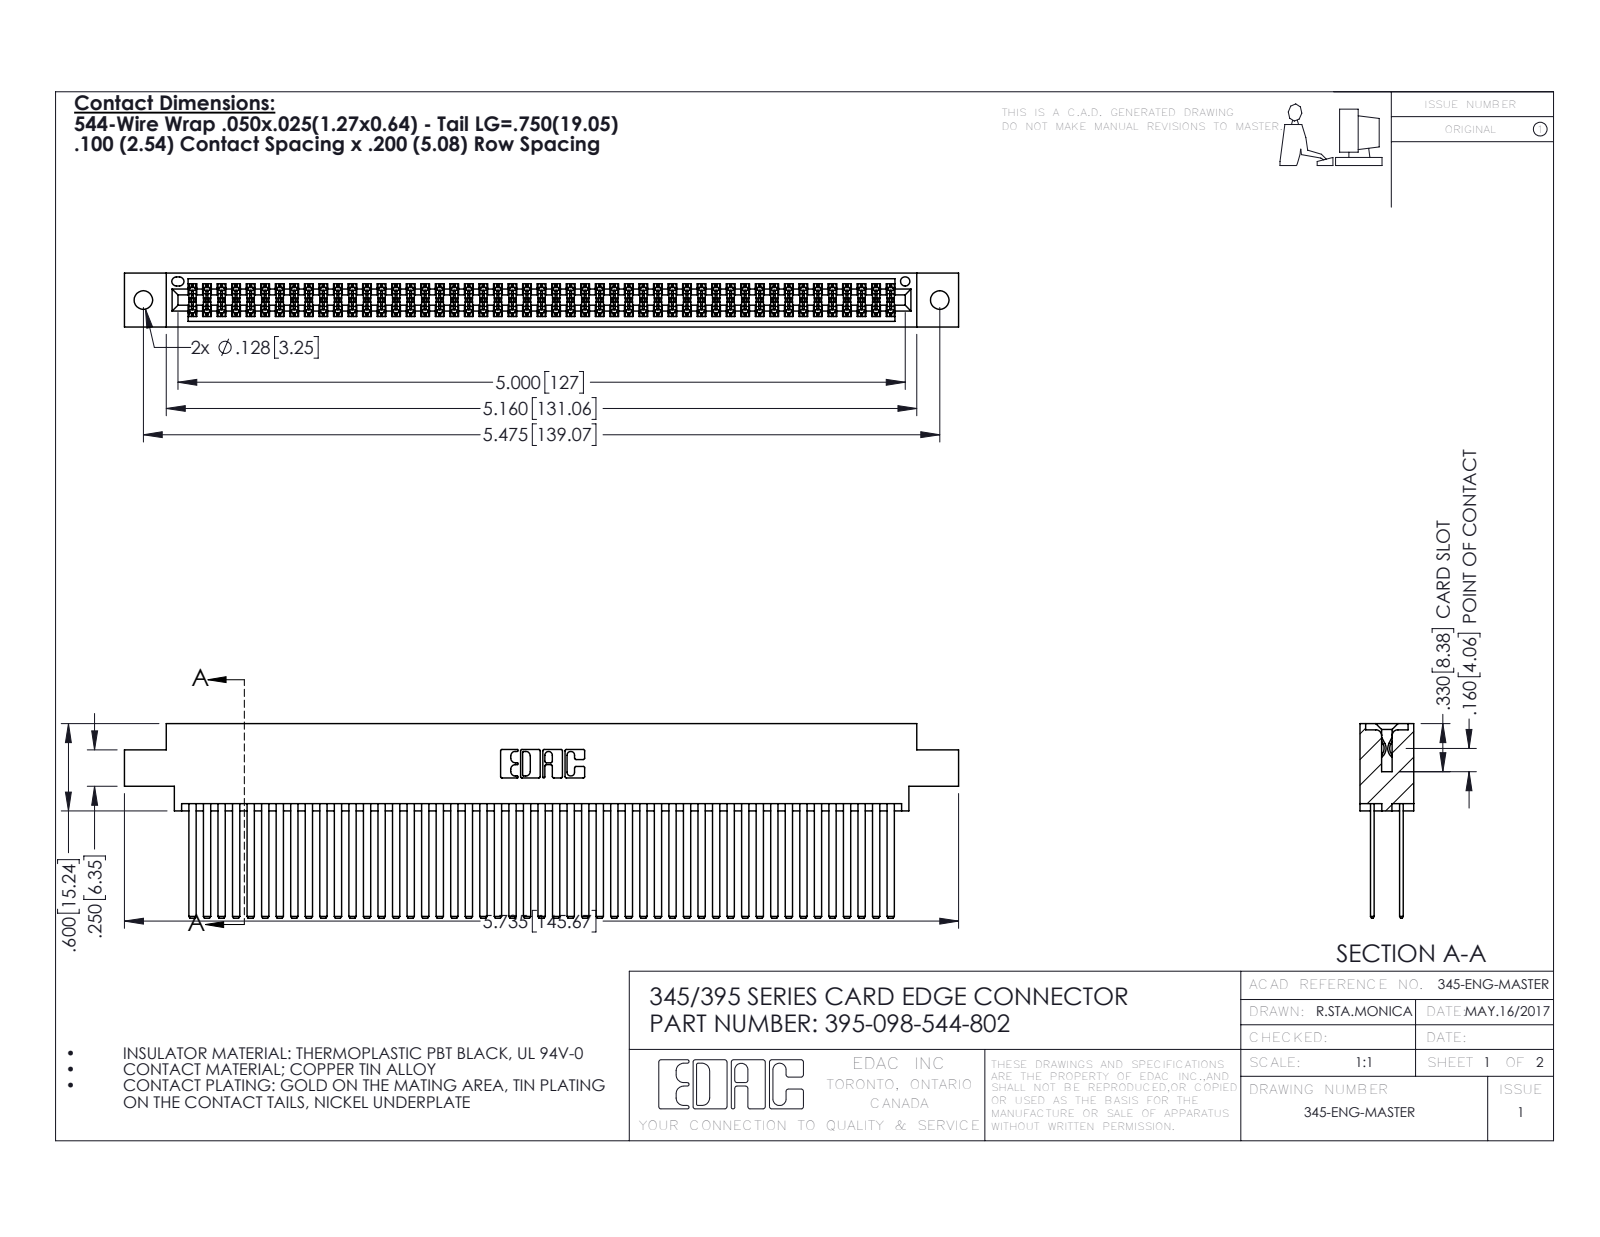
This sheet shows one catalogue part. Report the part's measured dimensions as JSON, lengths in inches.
{"part_name": "345 Part_0.170 Offset - 0.128 Dia; 345-292-001_345-293-144; 395-098-544-802", "step_written_by": "SolidWorks 2016 (CONFIG_CONTROL_DESIGN)", "units": "inches", "bodies": {"solids": 99, "faces": 4442, "planar": 2926, "cylindrical": 1516, "other": 0}, "overall_size": [5.735, 1.337, 0.37], "volume_in3": 0.942, "surface_area_in2": 41.62, "round_holes": [[0.128, 2], [0.064, 1]], "partial_cylinders_radius": [[0.006, 147], [0.01, 22], [0.007, 6], [0.031, 6], [0.026, 3], [0.014, 2], [0.019, 2], [0.022, 2]], "face_to_face_distances": [0.2, 0.025, 0.298, 0.072, 0.098, 0.272, 0.225, 0.175, 0.37, 0.15], "hole_center_spacings": [0.27, 5.239, 5.475]}
